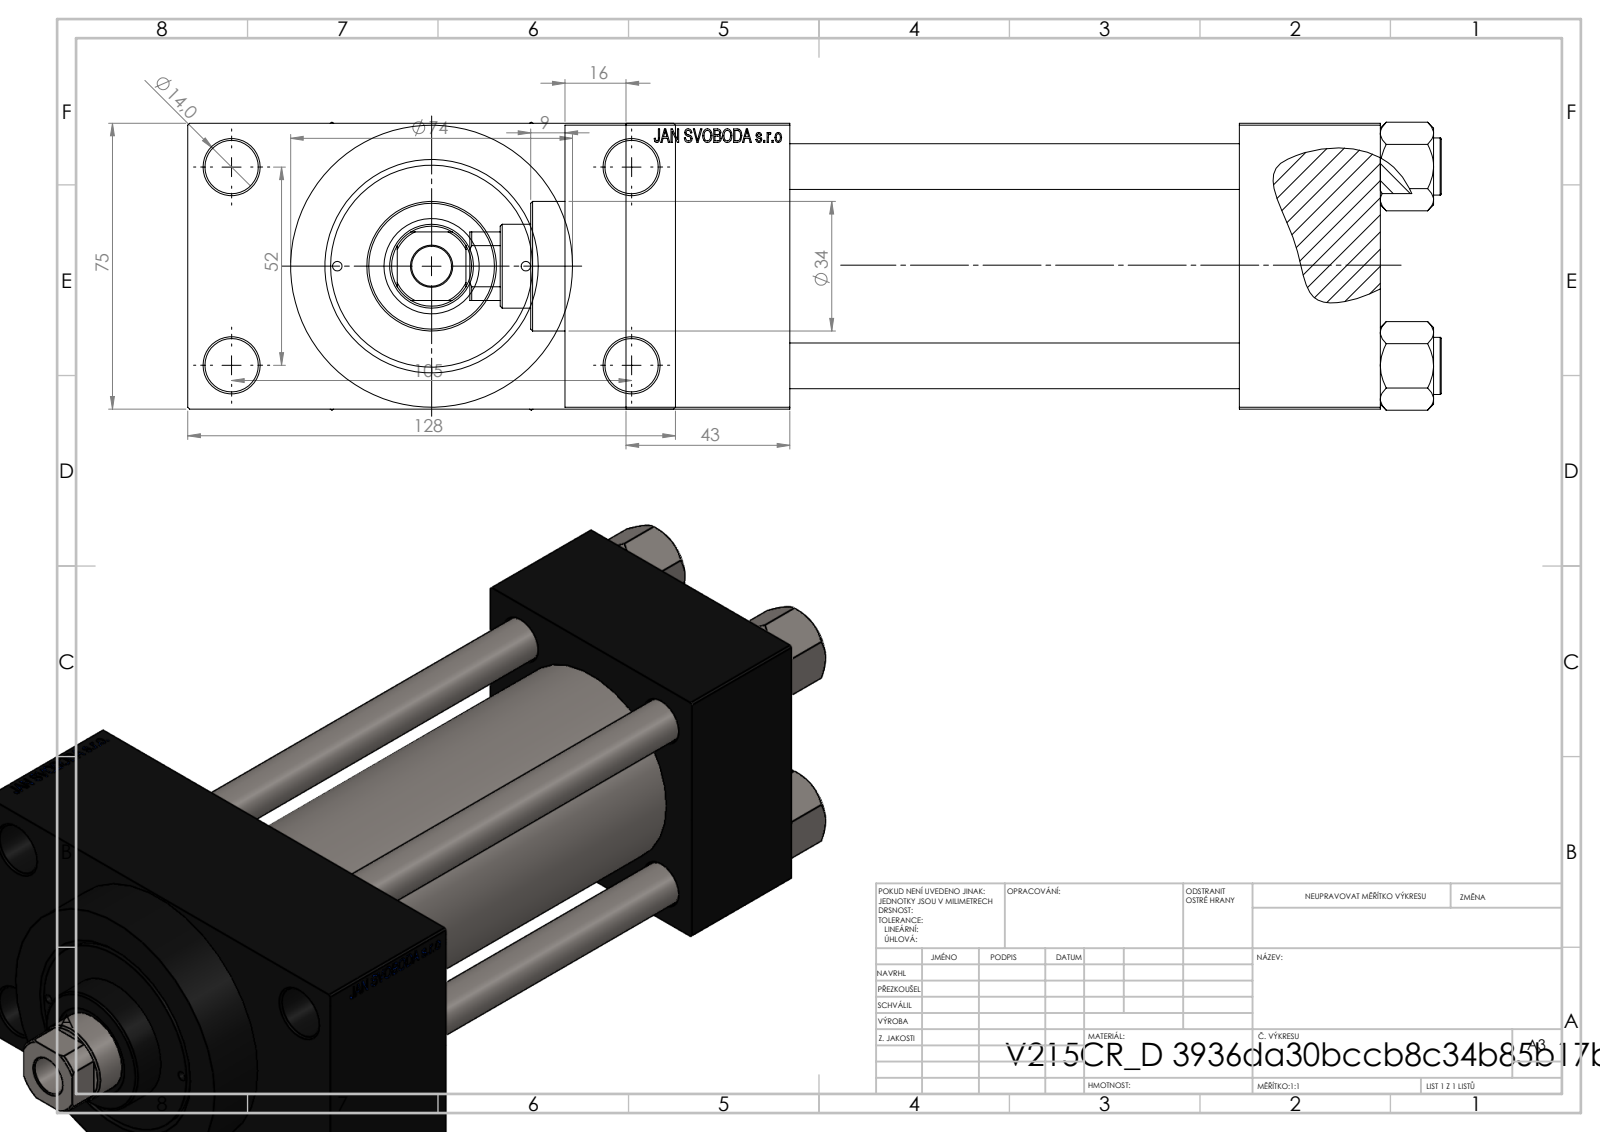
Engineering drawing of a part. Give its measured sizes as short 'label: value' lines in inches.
name: V215CR_D_TYCINKA; V215CR_D_Body; NUT_M5_D; V215CR_VCP_D (+1 more)
written by: SolidWorks 2019 (CONFIG_CONTROL_DESIGN)
unit: in
bodies: 11 solids, 1111 faces (499 planar, 92 cylindrical, 520 other)
size: 10.039 × 5.039 × 2.974
volume: 53.53 in³; area: 309.7 in²
holes: 4× ⌀0.472, 4× ⌀0.551, 2× ⌀0.098, 2× ⌀0.276, 2× ⌀0.825, 2× ⌀1.181, 1× ⌀0.413, 1× ⌀0.866, 1× ⌀0.984, 1× ⌀1.614, 1× ⌀1.969, 1× ⌀2.087
bosses: 4× ⌀0.591, 1× ⌀2.913, 1× ⌀2.205, 1× ⌀1.339
rounds: 1× R0.413
face distances: 2.953, 4.646, 1.457, 6.102, 1.043, 7.795, 6.339, 1.693, 3.996, 0.63
hole spacings: 1.031, 1.037, 1.456, 1.497, 2.059, 2.253, 2.3, 2.307
